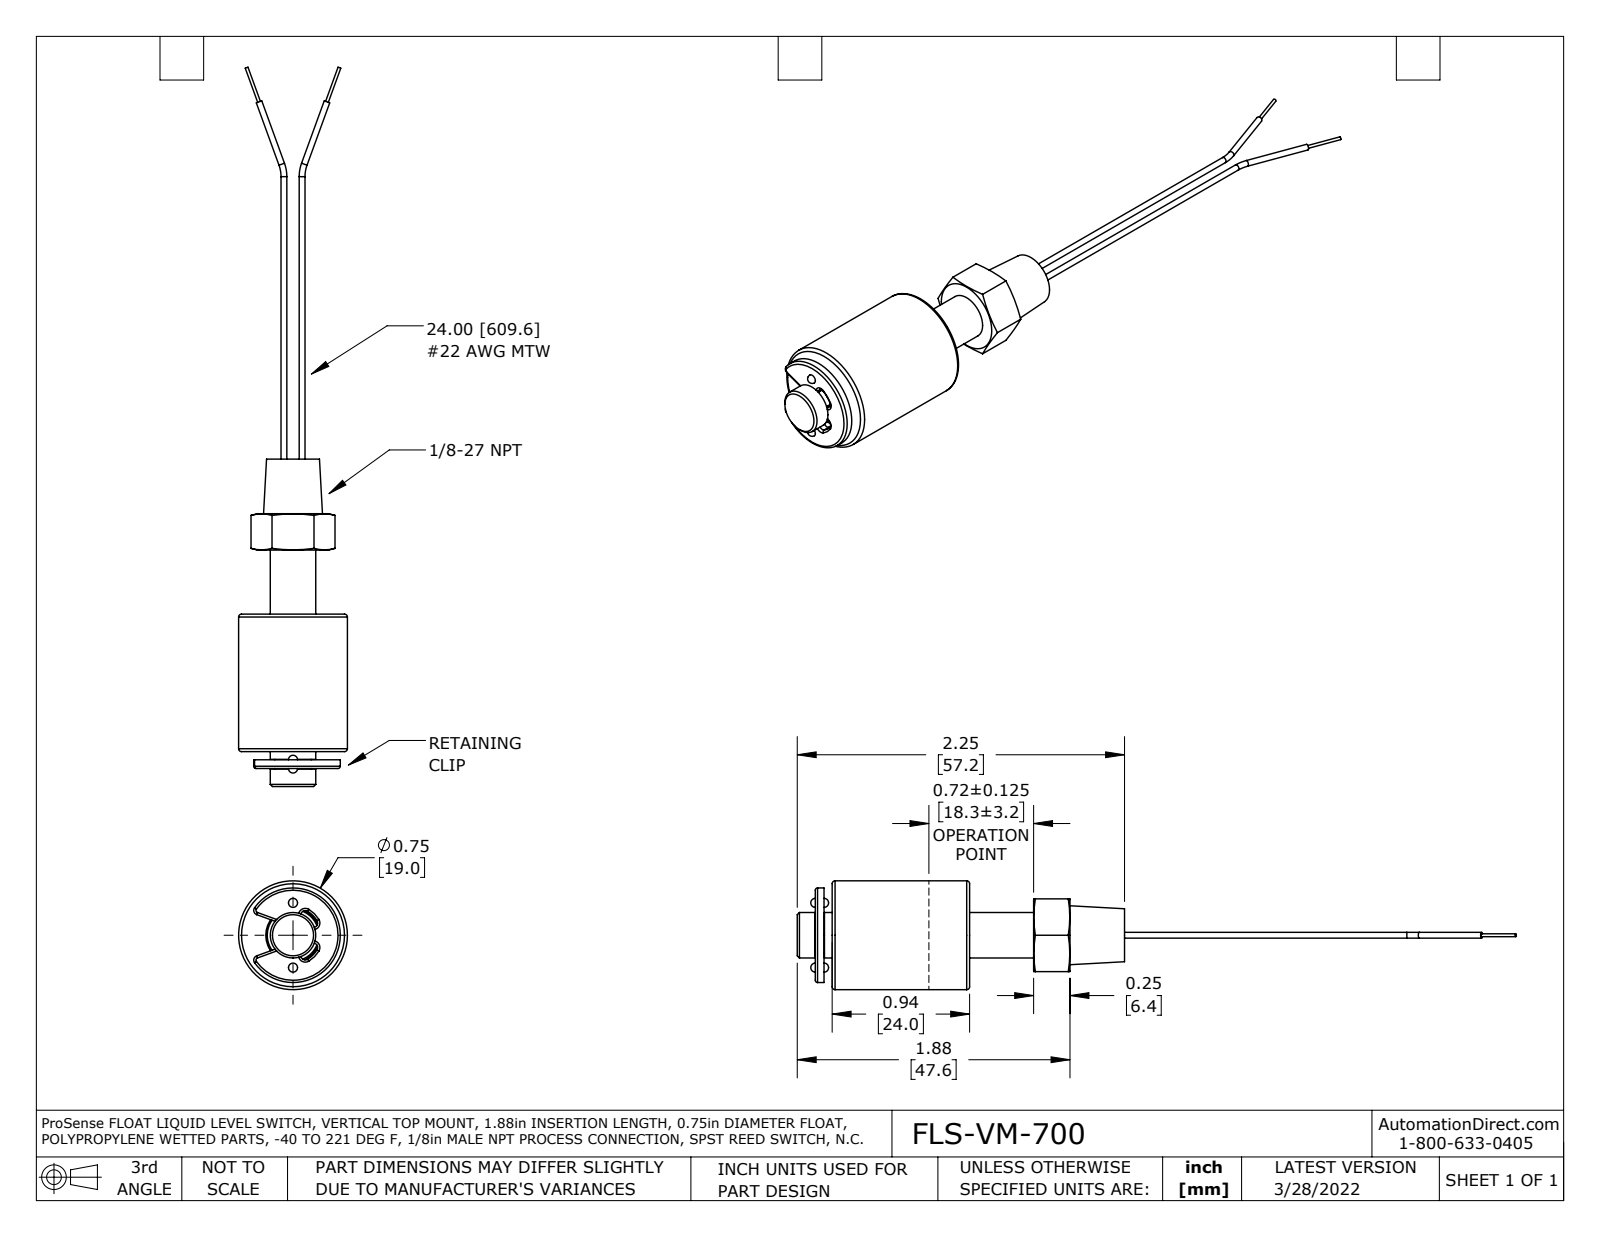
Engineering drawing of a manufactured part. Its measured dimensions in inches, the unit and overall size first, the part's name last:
Units: inches
Overall size (bounding box): 4.943 × 0.748 × 0.748
Round holes (diameter × count): ⌀0.01 ×2, ⌀0.354 ×1
Round bosses / shafts (diameter × count): ⌀0.04 ×4, ⌀0.02 ×2, ⌀0.748 ×1, ⌀0.65 ×1, ⌀0.313 ×1, ⌀0.25 ×1
Partial cylindrical surfaces — rounded edges, fillets, slot ends (radius × count): R0.016 ×10, R0.031 ×8, R0.127 ×1, R0.193 ×1
Main face-to-face distances: 0.945, 0.5, 1.001, 0.056, 1.061, 0.116, 0.06, 0.44, 1.385, 1.441
Hole centre spacings: 0.063, 0.125
Volume: 0.493 in³ · Surface area: 9.924 in²
Bodies: 7 solids, 150 faces (33 planar, 57 cylindrical, 60 other)
Part name (STEP PRODUCT): ADM8000-75 nc coord fxt
STEP written by: SolidWorks 2021 (AUTOMOTIVE_DESIGN)
